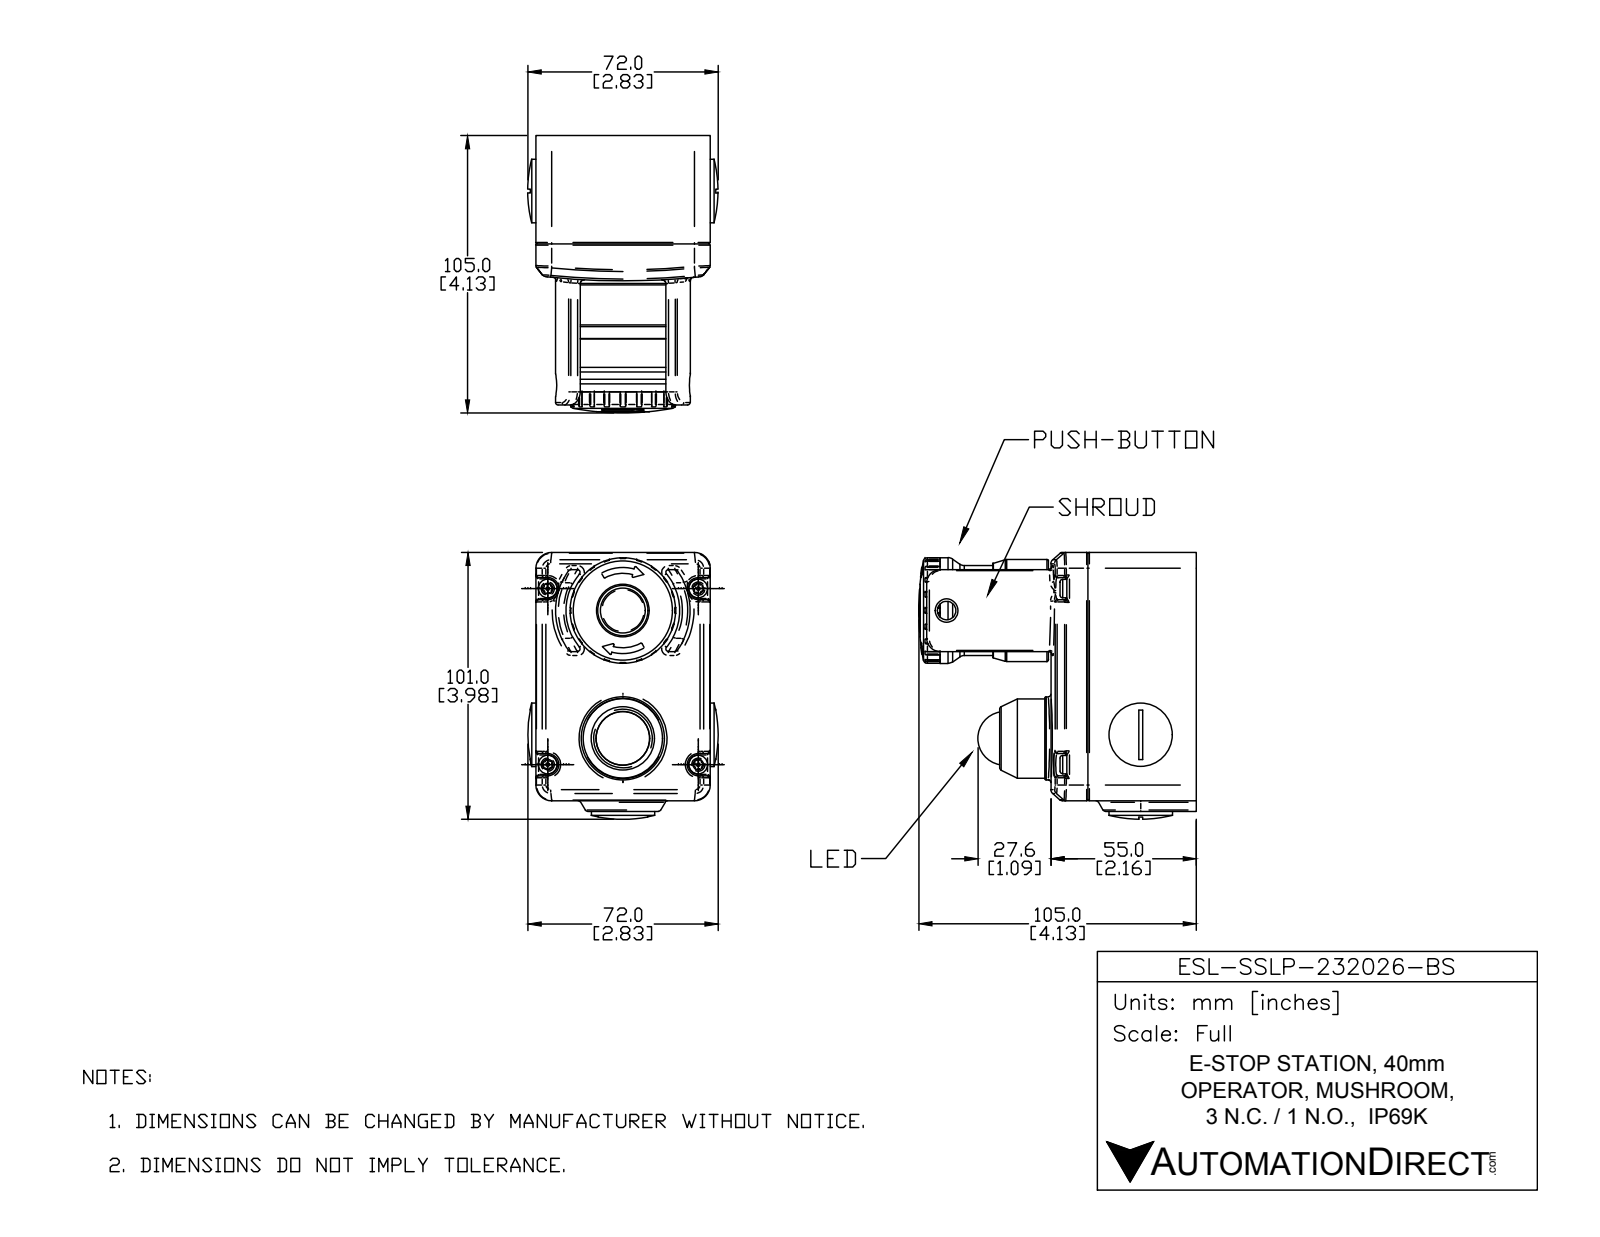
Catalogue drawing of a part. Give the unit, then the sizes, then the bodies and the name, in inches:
Units: inches
Overall size (bounding box): 4.134 × 3.976 × 2.834
Round holes (diameter × count): ⌀0.177 ×4, ⌀0.276 ×1, ⌀1.104 ×1, ⌀1.224 ×1, ⌀1.457 ×1
Round bosses / shafts (diameter × count): ⌀0.276 ×4, ⌀0.039 ×4, ⌀0.945 ×2, ⌀1.575 ×1, ⌀1.52 ×1, ⌀1.339 ×1, ⌀1.236 ×1, ⌀1.181 ×1
Partial cylindrical surfaces — rounded edges, fillets, slot ends (radius × count): R0.004 ×80, R0.03 ×24, R0.02 ×14, R0.039 ×13, R0.059 ×6, R0.008 ×4, R0.165 ×4, R0.236 ×4
Main face-to-face distances: 1.614, 2.598, 2.205, 0.591, 3.858, 0.157, 3.701, 2.236, 0.622, 0.031
Hole centre spacings: 1.235, 1.269, 2.126, 2.749, 2.807, 3.228, 3.865, 1.906
Volume: 23.35 in³ · Surface area: 112.8 in²
Bodies: 13 solids, 797 faces (227 planar, 287 cylindrical, 283 other)
Part name (STEP PRODUCT): ESL-SSLP-232026-BS
STEP written by: SolidWorks 2016 (AUTOMOTIVE_DESIGN)
